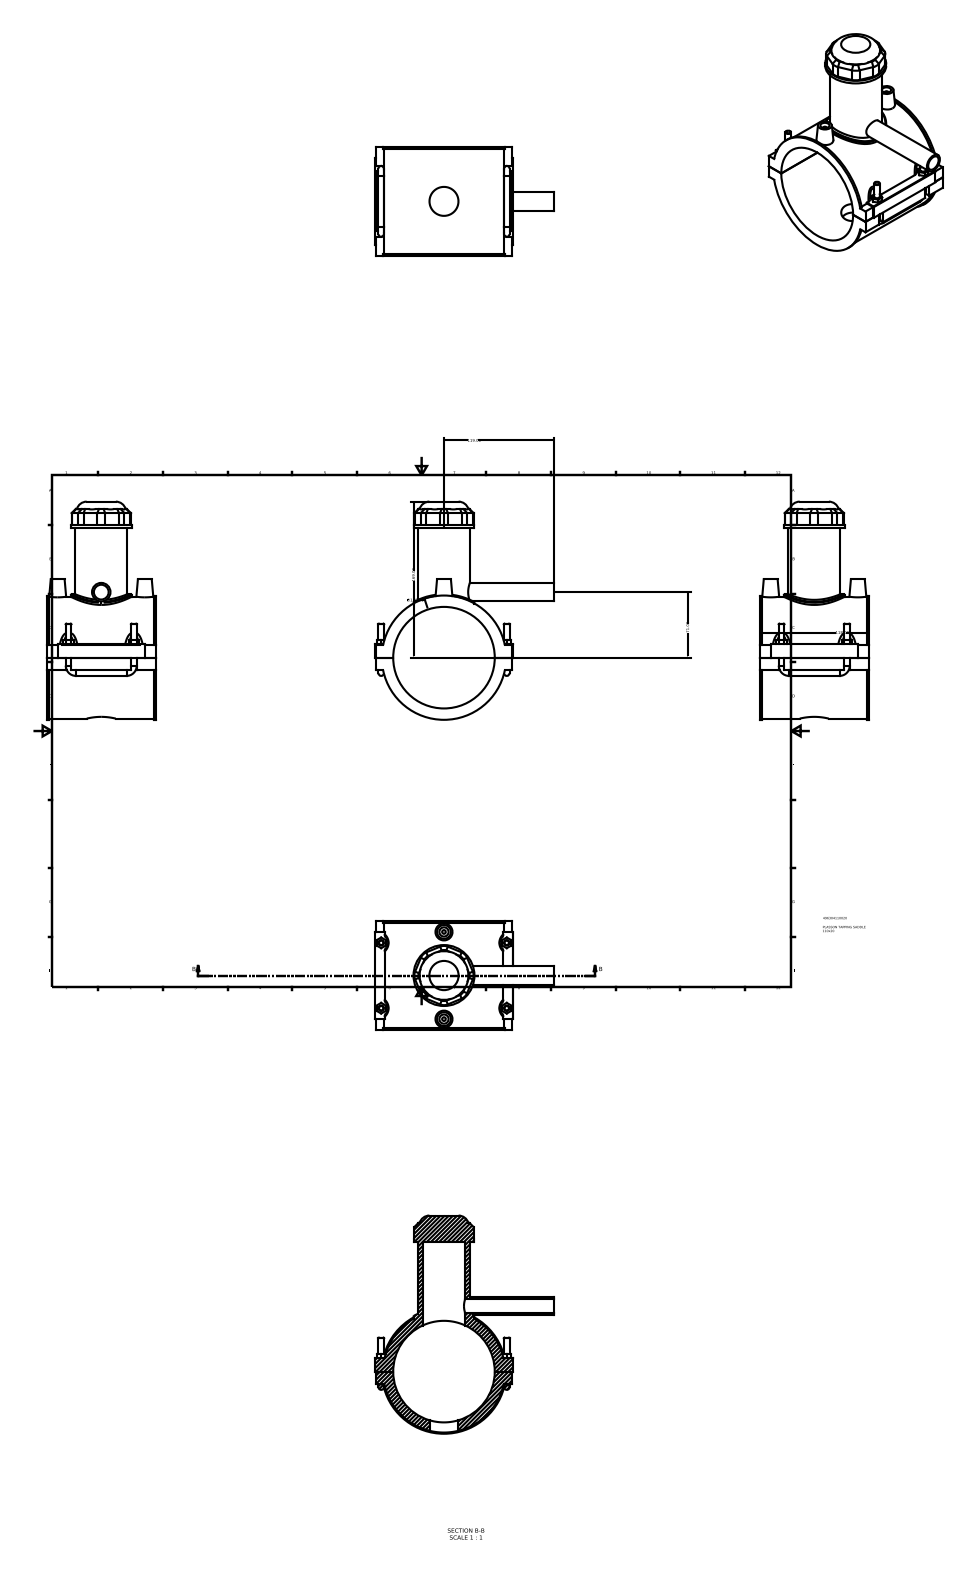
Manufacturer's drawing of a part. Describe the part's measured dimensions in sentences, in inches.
The part is named "496304110020". Its 3-D file was written by "Autodesk Inventor 2015 (AUTOMOTIVE_DESIGN)". It is 1 solid with 188 faces: 117 planar, 47 cylindrical and 24 other. Overall it measures 9.304 by 7.638 by 4.646 inches. Its volume is 42.04 cubic inches and its surface area 256.7 square inches. Round holes: 2 of diameter 0.394, 1 of diameter 0.63, 1 of diameter 1.235, 1 of diameter 1.819, 1 of diameter 4.331. Round bosses or shafts: 6 of diameter 0.236, 2 of diameter 0.157, 1 of diameter 5.301, 1 of diameter 5.197, 1 of diameter 2.598, 1 of diameter 2.209, 1 of diameter 0.787. Partial cylindrical surfaces (rounded edges, fillets, slot ends): 8 of radius 0.433, 4 of radius 0.118, 4 of radius 0.295, 1 of radius 0.02, 1 of radius 2.702. The main face-to-face distances are 4.646, 0.039, 6.073, 5.866, 5.533, 5.53, 1.122, 0.539, 0.543, 0.583. The hole center spacings are 1.858, 3.717.
